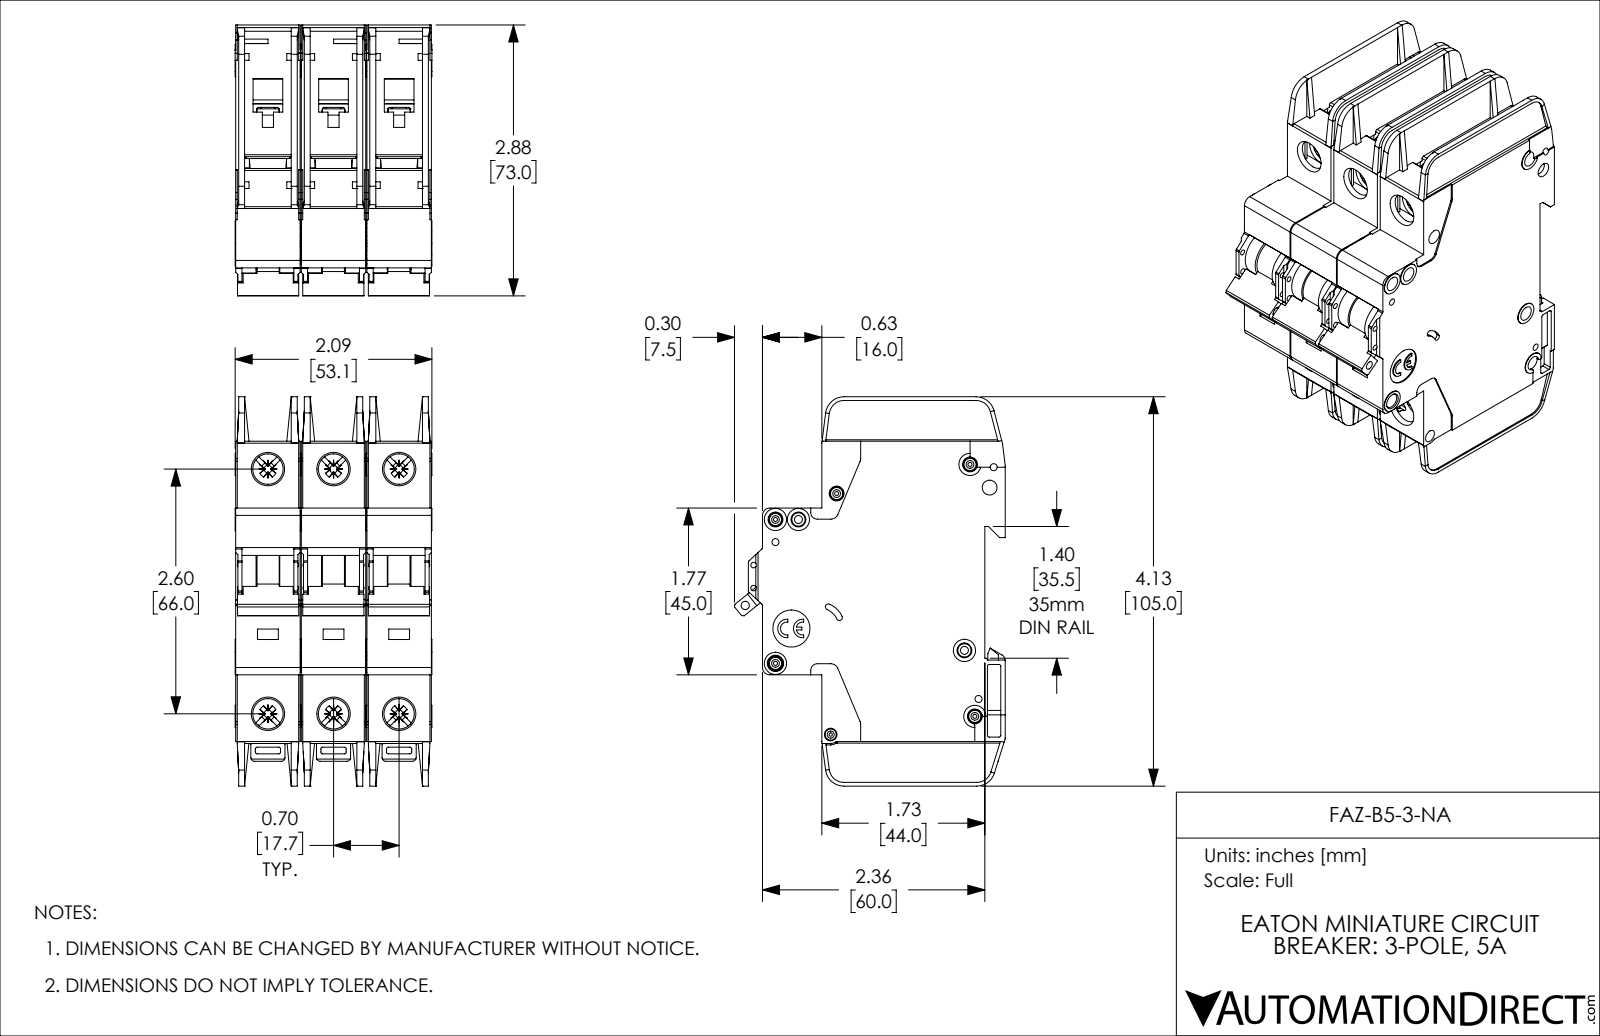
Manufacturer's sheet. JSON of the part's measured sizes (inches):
{"part_name": "FAZ-B5-3-NA", "step_written_by": "SolidWorks 2019 (AUTOMOTIVE_DESIGN)", "units": "inches", "bodies": {"solids": 3, "faces": 3381, "planar": 2013, "cylindrical": 1071, "other": 297}, "overall_size": [4.134, 2.876, 2.091], "volume_in3": 14.05, "surface_area_in2": 123, "round_holes": [[0.157, 8], [0.323, 6], [0.043, 5], [0.075, 4], [0.059, 2], [0.085, 2], [0.035, 1], [0.089, 1], [0.098, 1], [0.134, 1], [0.394, 1]], "round_bosses_or_shafts": [[0.13, 5], [0.236, 4], [0.118, 4], [0.098, 3]], "partial_cylinders_radius": [[0.02, 72], [0.016, 30], [0.039, 18], [0.043, 12], [0.079, 12], [0.008, 6], [0.01, 6], [0.028, 6]], "face_to_face_distances": [0.697, 0.047, 1.394, 0.685, 0.591, 1.382, 0.744, 0.65, 0.106, 0.094], "hole_center_spacings": [0.697, 2.69, 2.598, 0.244, 0.537, 0.87, 1.394, 2.948]}
